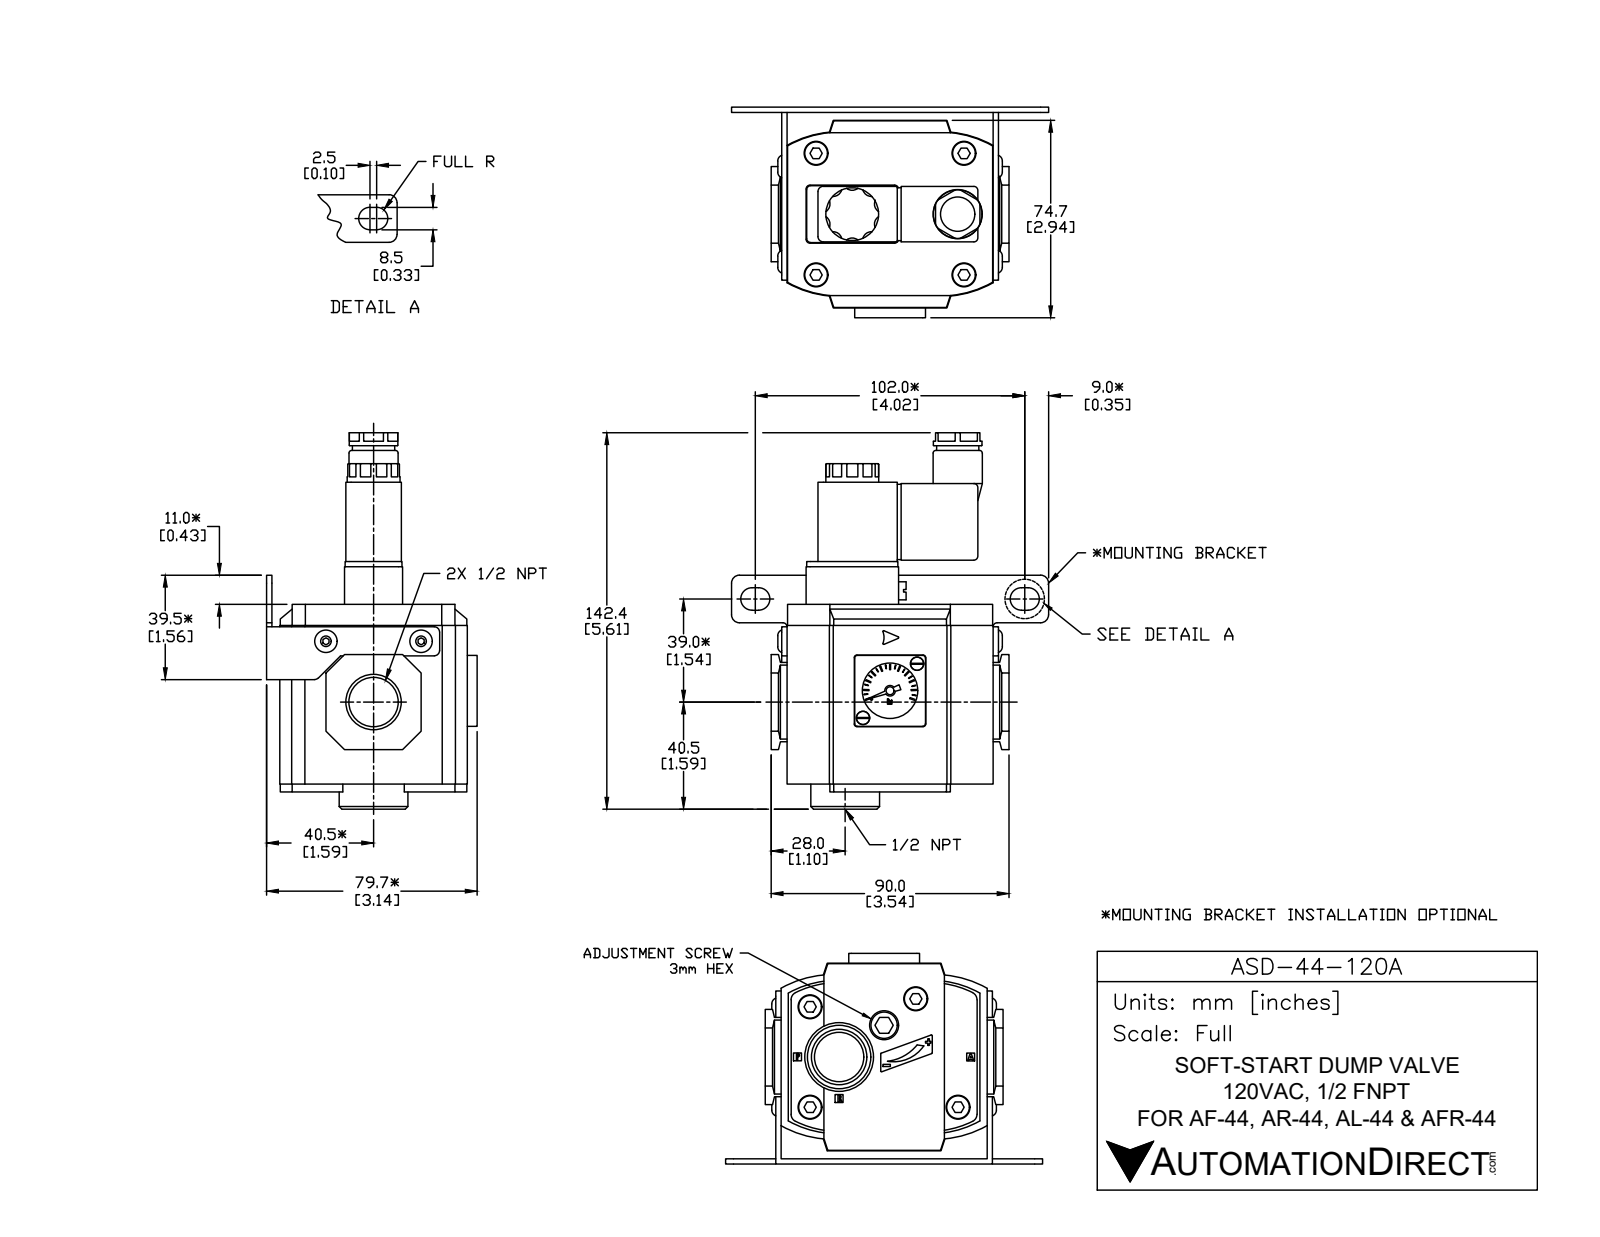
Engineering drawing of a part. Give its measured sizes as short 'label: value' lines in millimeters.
name: ASD-44-120A
written by: SolidWorks 2015 (CONFIG_CONTROL_DESIGN)
unit: mm
bodies: 22 solids, 554 faces (347 planar, 164 cylindrical, 43 other)
size: 142.4 × 120 × 79.7
volume: 419 336 mm³; area: 84 834 mm²
holes: 8× ⌀6, 8× ⌀9, 2× ⌀3, 1× ⌀10, 1× ⌀11, 1× ⌀13, 1× ⌀17.86, 1× ⌀18.63, 1× ⌀21, 1× ⌀26
bosses: 8× ⌀8, 2× ⌀2.5, 1× ⌀20, 1× ⌀18.6, 1× ⌀18.4, 1× ⌀16, 1× ⌀4
rounds: 10× R1.5, 10× R3.16, 6× R1, 6× R3, 4× R0.73, 4× R1.25, 4× R4.25, 4× R39.8
face distances: 60, 3, 2, 68, 8, 71, 4.5, 46, 20.5, 25
hole spacings: 4, 42, 56, 56.14, 70, 14.5, 21.95, 23.12
